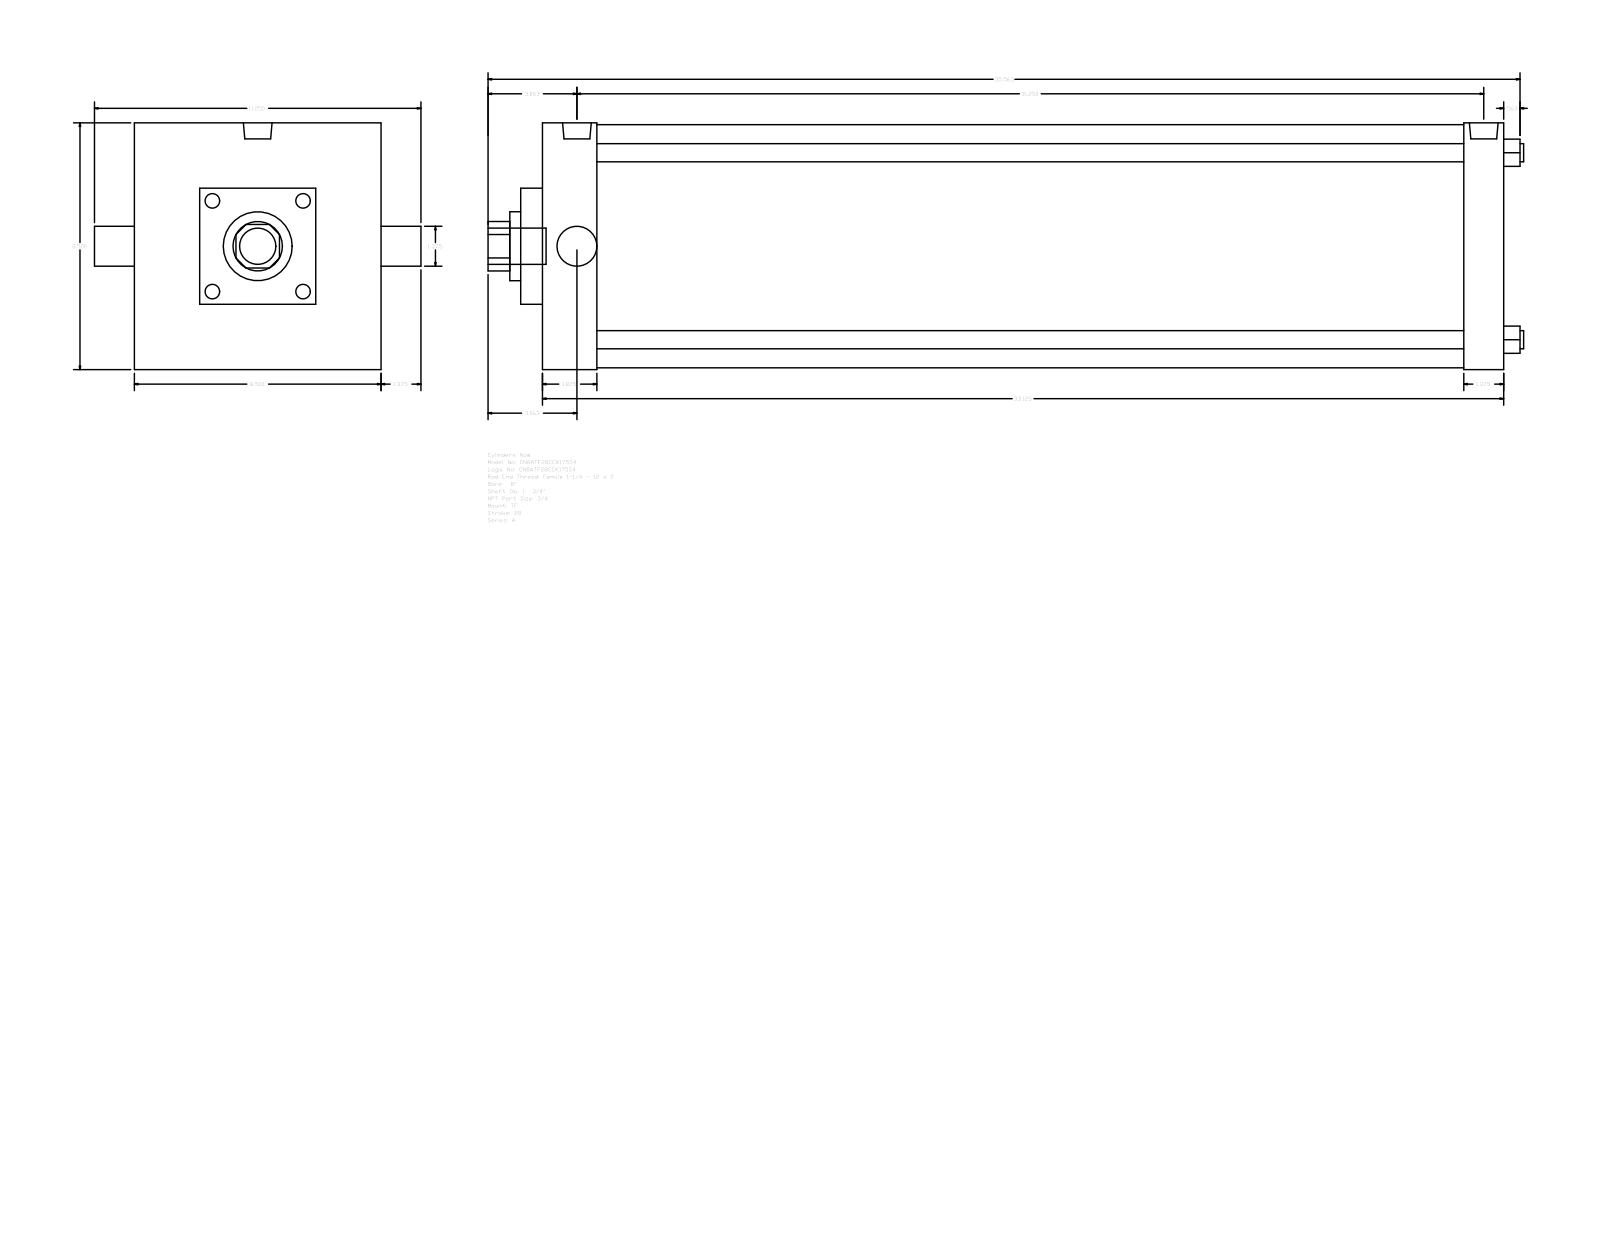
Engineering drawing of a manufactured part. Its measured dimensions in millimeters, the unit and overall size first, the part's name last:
Units: millimetres
Overall size (bounding box): 906.46 × 285.75 × 215.9
Round holes (diameter × count): ⌀15.88 ×4, ⌀34.92 ×1, ⌀44.45 ×1, ⌀60.33 ×1, ⌀212.72 ×1
Round bosses / shafts (diameter × count): ⌀15.08 ×3, ⌀25.12 ×2, ⌀31.75 ×1
Partial cylindrical surfaces — rounded edges, fillets, slot ends (radius × count): R21.63 ×1
Main face-to-face distances: 841.38, 215.9, 34.92, 47.63, 793.75, 806.46, 758.83, 19.05, 57.15, 158.75
Hole centre spacings: 115.67, 163.58, 231.34
Bodies: 0 solids, 89 faces (65 planar, 24 cylindrical, 0 other)
Part name (STEP PRODUCT): A_TF__0800_1.75
STEP written by: GSSL Pune (CONFIG_CONTROL_DESIGN)
